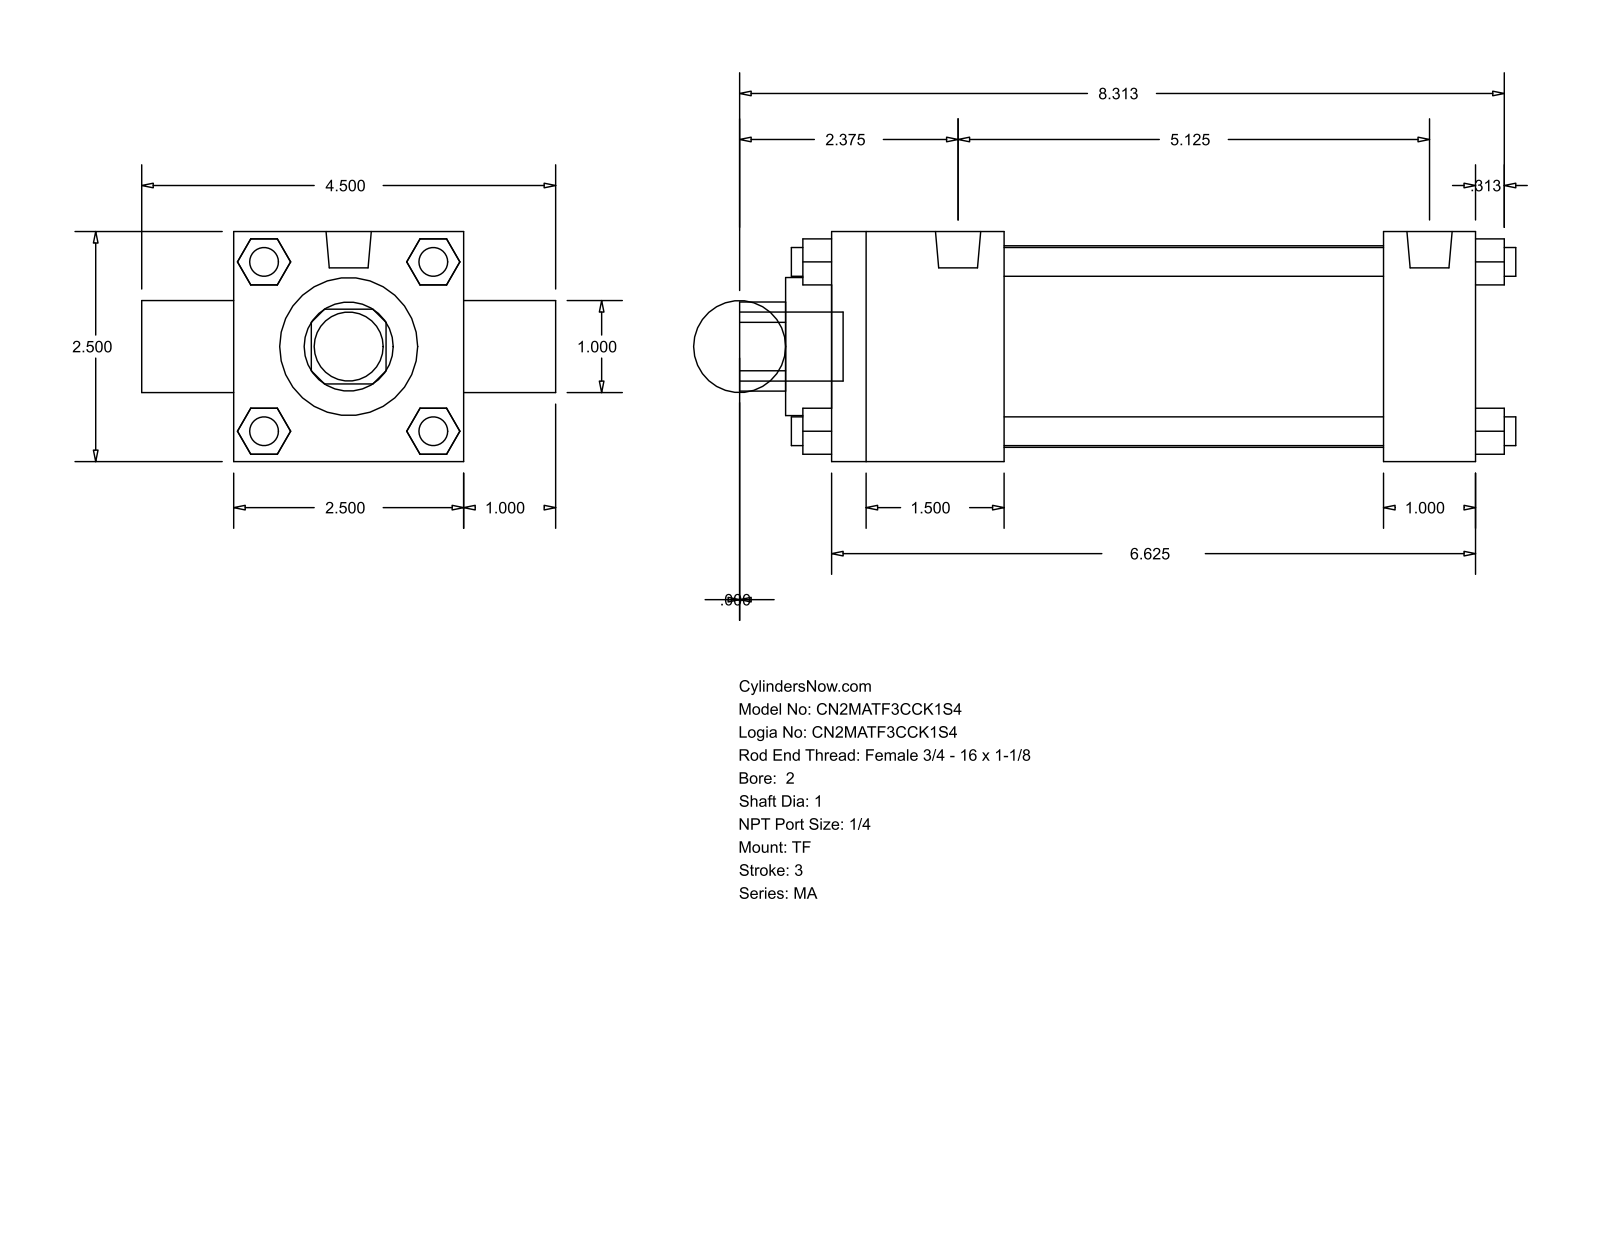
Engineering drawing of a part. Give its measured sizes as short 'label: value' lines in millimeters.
name: MA_TF__0200_1
written by: GSSL Pune (CONFIG_CONTROL_DESIGN)
unit: mm
bodies: 0 solids, 120 faces (92 planar, 28 cylindrical, 0 other)
size: 214.31 × 114.3 × 63.5
holes: 2× ⌀25.4, 1× ⌀38.1, 1× ⌀55.63
bosses: 7× ⌀7.94, 2× ⌀12.49, 1× ⌀19.05
rounds: 1× R12.29
face distances: 63.5, 25.4, 177.8, 12.7, 47.63, 152.4, 104.77, 130.17, 88.9, 40.47
